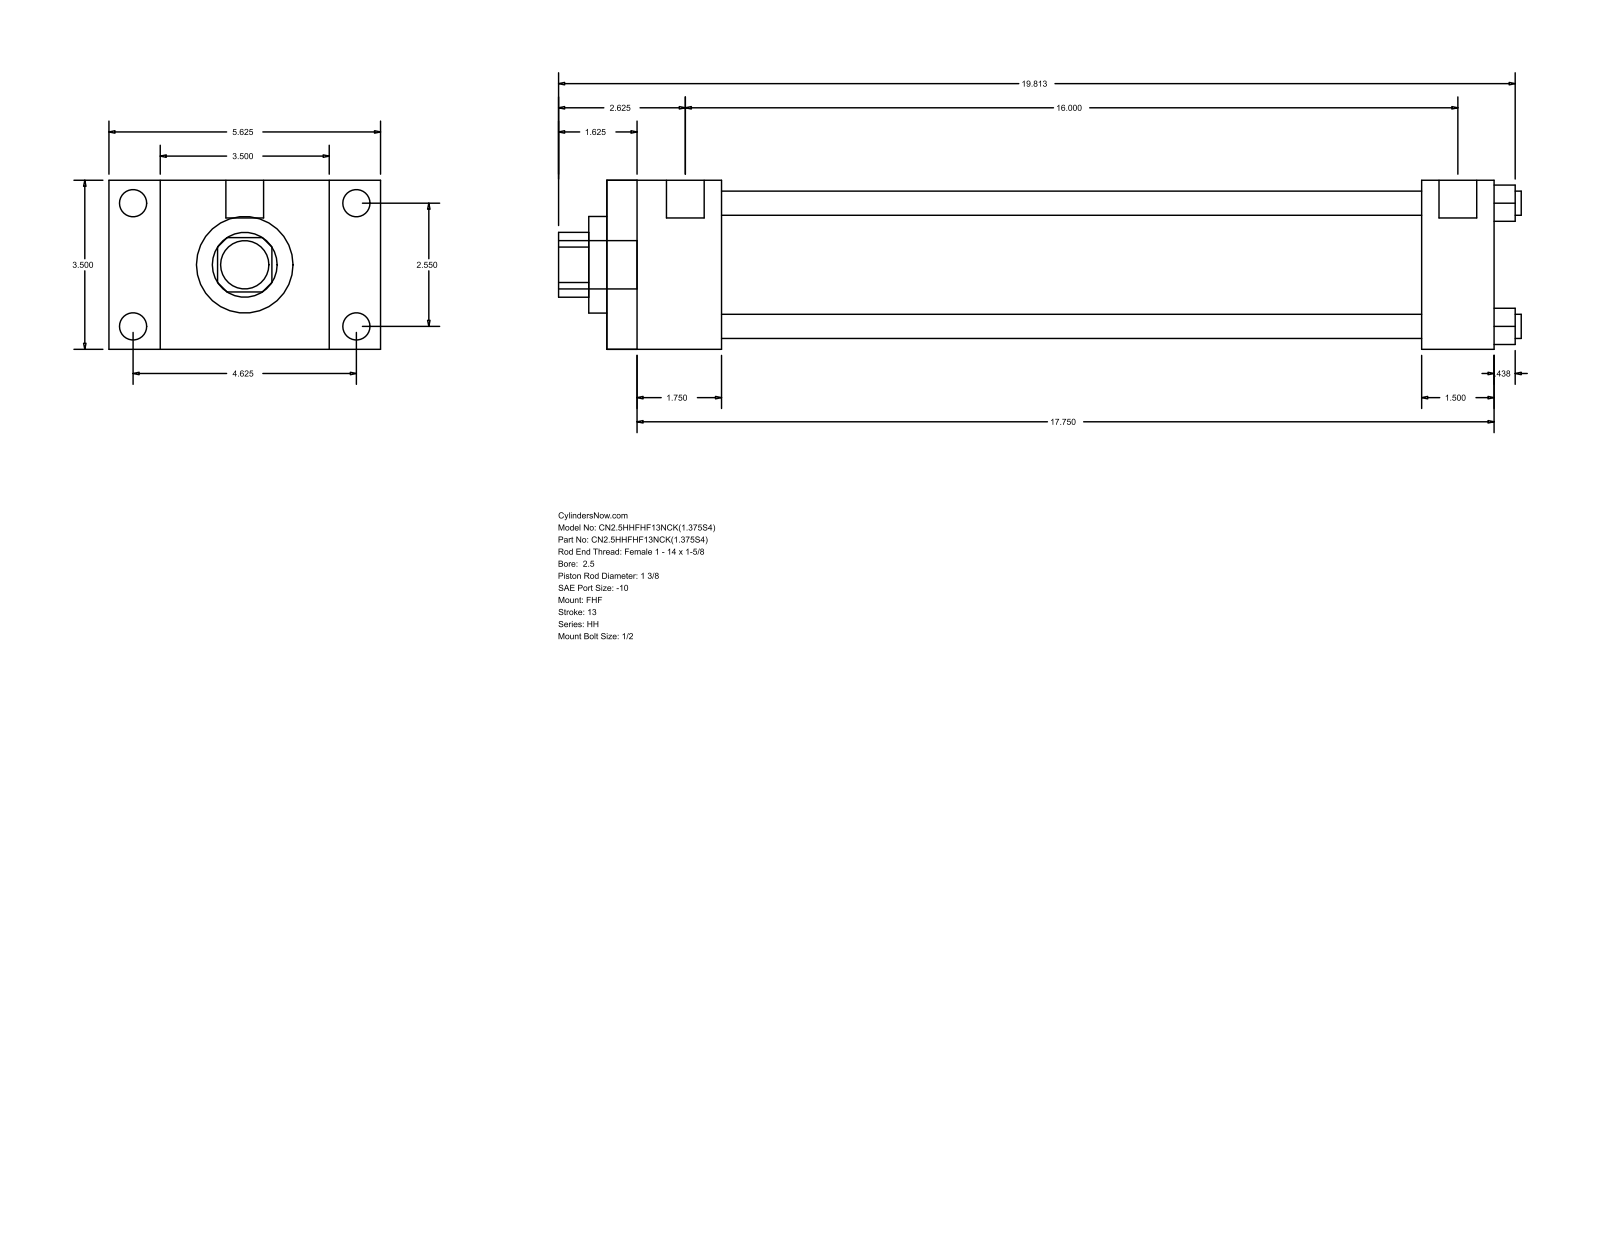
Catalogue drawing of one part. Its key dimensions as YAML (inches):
part_name: "HH_FHF__0250_1.375"
step_written_by: "GSSL Pune (CONFIG_CONTROL_DESIGN)"
units: inches
bodies: {solids: 0, faces: 88, planar: 60, cylindrical: 28, other: 0}
overall_size: [19.937, 5.625, 3.5]
round_holes:
  - {diameter: 0.5, count: 4}
  - {diameter: 1.375, count: 1}
  - {diameter: 2, count: 1}
  - {diameter: 2.875, count: 1}
round_bosses_or_shafts:
  - {diameter: 0.563, count: 4}
  - {diameter: 0.219, count: 4}
  - {diameter: 0.781, count: 2}
  - {diameter: 1, count: 1}
partial_cylinders:
  - {radius: 0.672, count: 1}
face_to_face_distances: [3.5, 2.375, 1.063, 4.563, 18.375, 16, 5.625, 16.875, 14.5, 1.5]
hole_center_spacings: [1.803, 2.55, 3.606]
